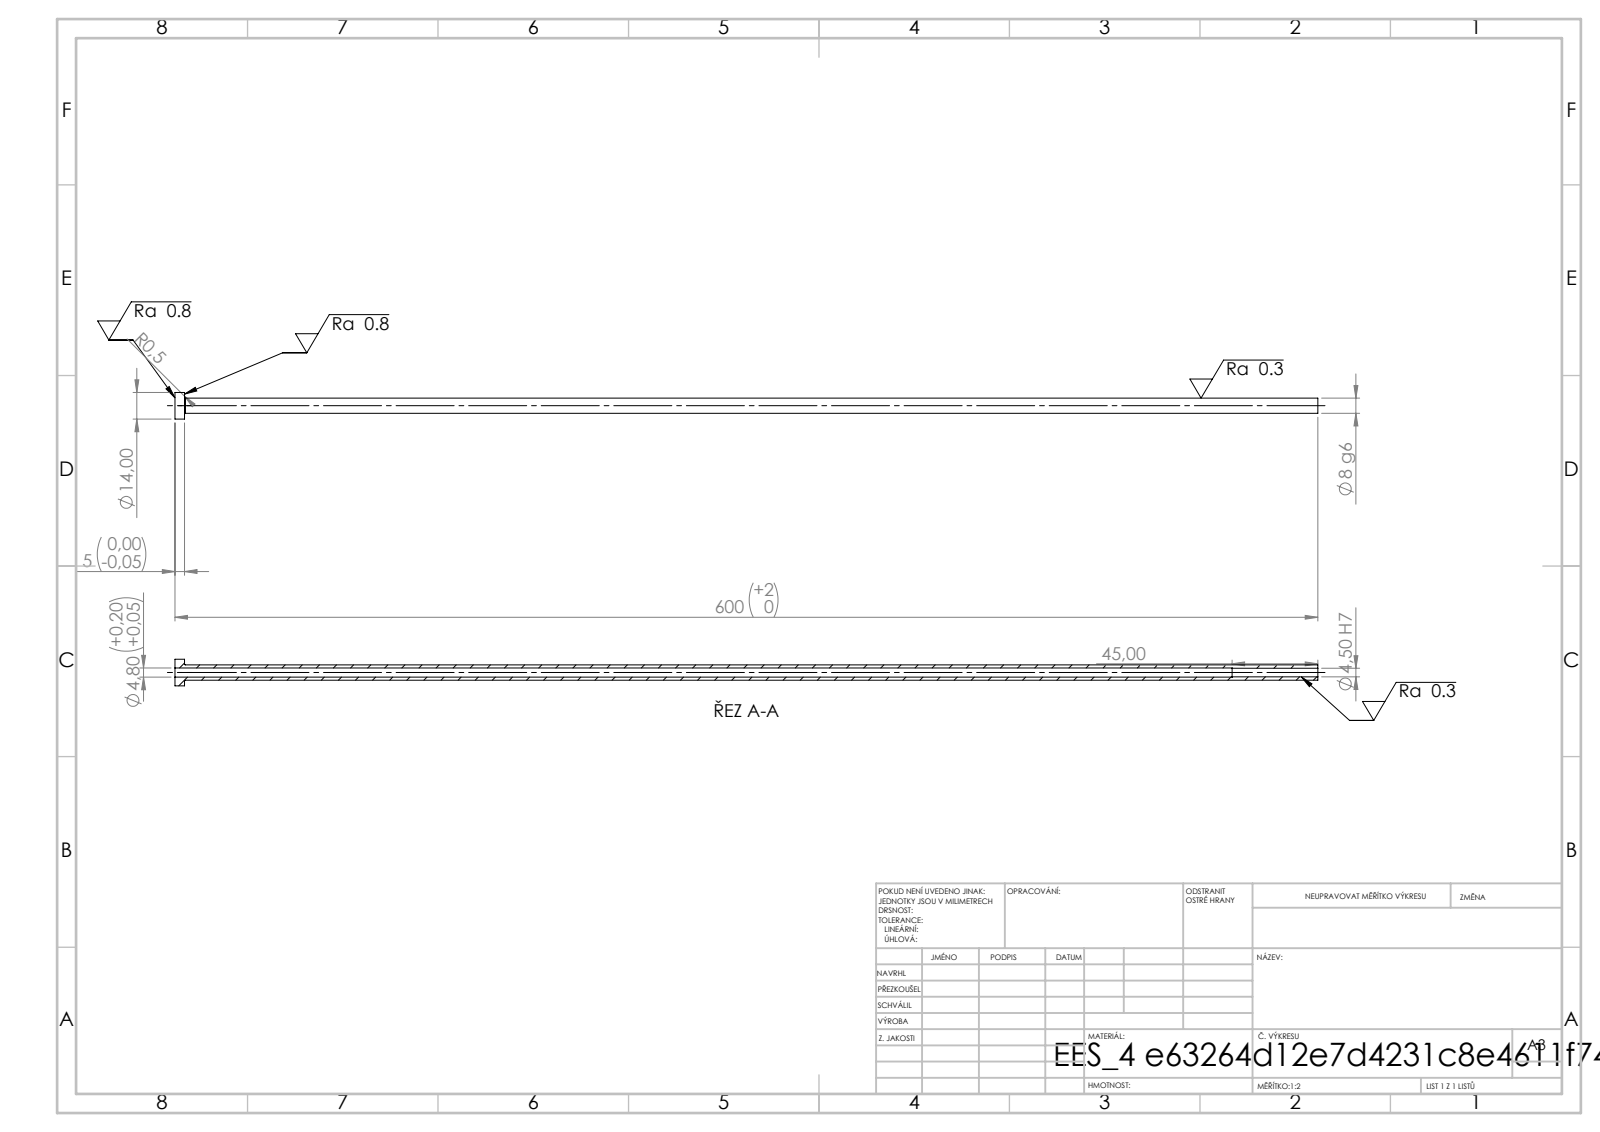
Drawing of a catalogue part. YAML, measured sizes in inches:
step_written_by: "SolidWorks 2019 (CONFIG_CONTROL_DESIGN)"
units: inches
bodies: {solids: 1, faces: 14, planar: 4, cylindrical: 8, other: 2}
overall_size: [23.622, 0.551, 0.551]
volume: 1.216
surface_area: 37.9
round_holes:
  - {diameter: 0.177, count: 1}
  - {diameter: 0.189, count: 1}
round_bosses_or_shafts:
  - {diameter: 0.551, count: 1}
  - {diameter: 0.315, count: 1}
face_to_face_distances: [0.197, 23.622, 23.425, 21.85, 21.654, 1.772]
